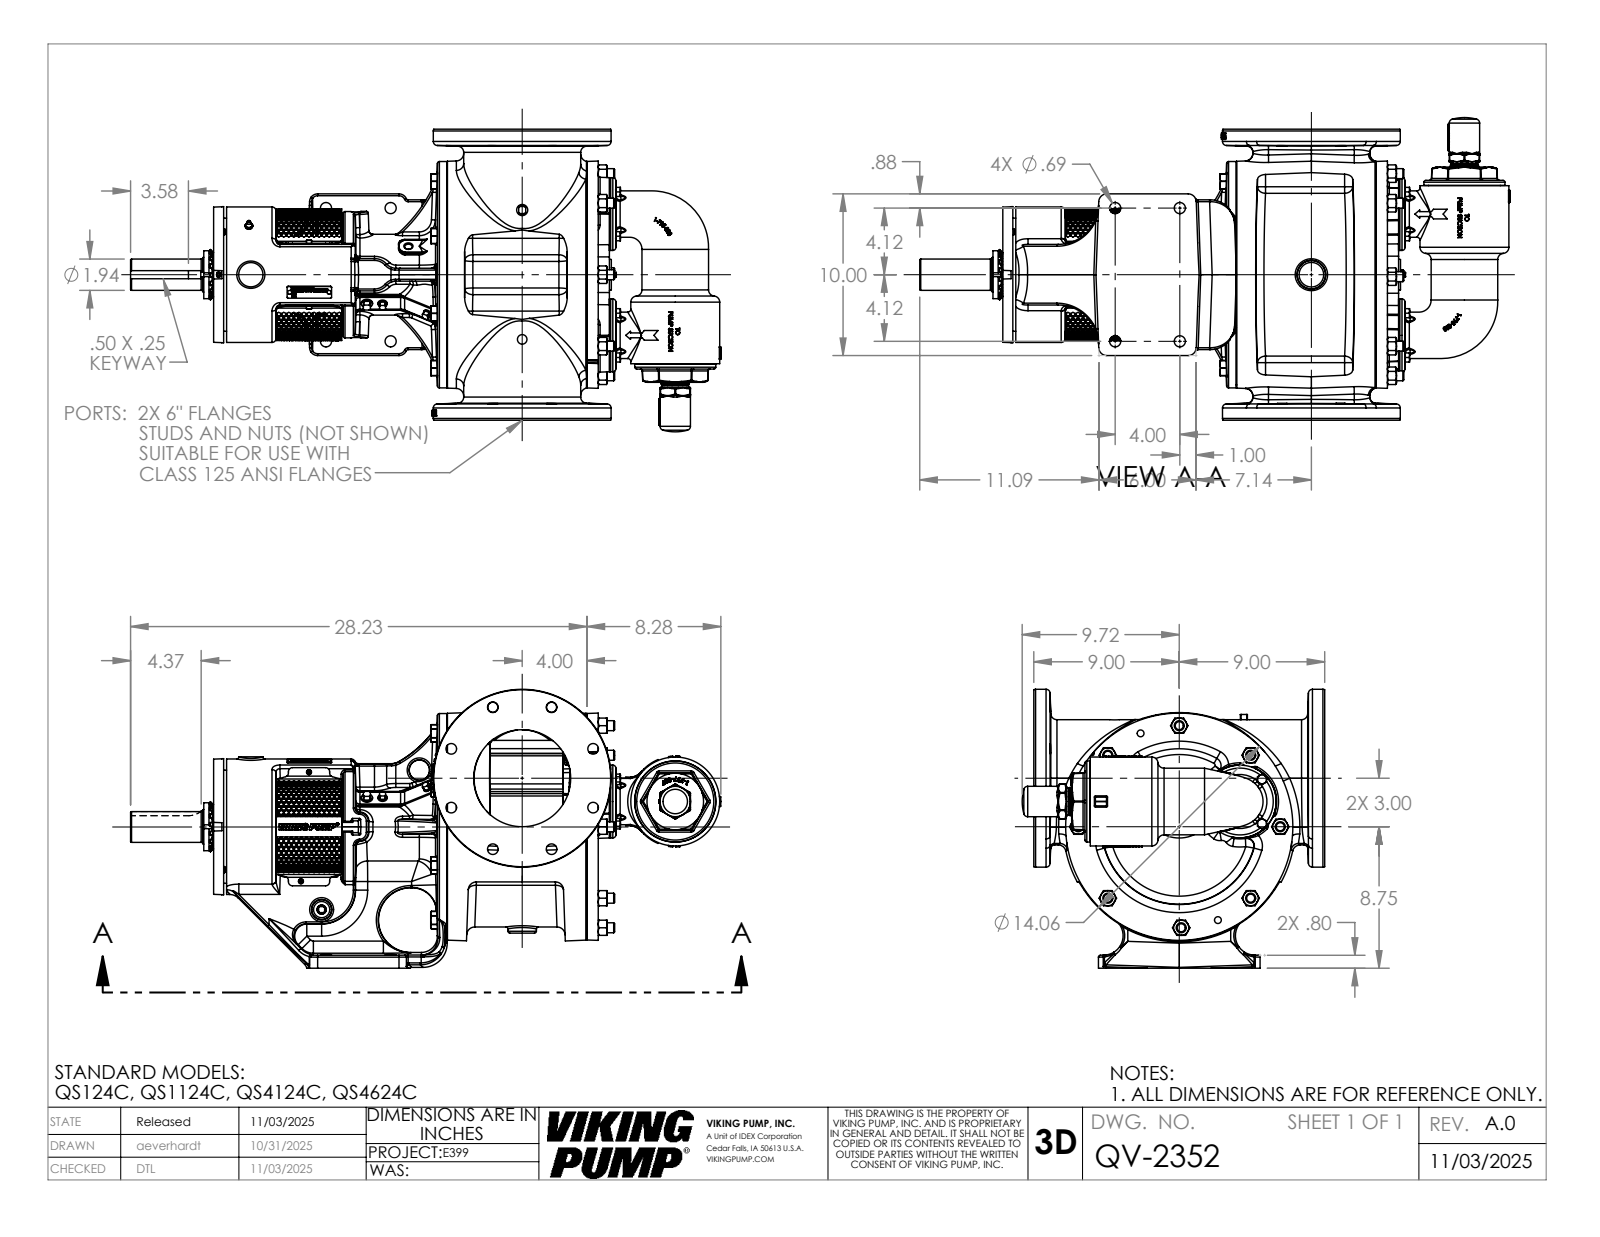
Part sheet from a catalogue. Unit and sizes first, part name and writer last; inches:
Units: inches
Overall size (bounding box): 36.523 × 22.94 × 17.25
Round holes (diameter × count): ⌀0.266 ×8, ⌀0.406 ×8, ⌀0.41 ×8, ⌀0.656 ×8, ⌀1.157 ×8, ⌀0.25 ×6, ⌀0.688 ×4, ⌀0.159 ×2, ⌀0.313 ×2, ⌀0.422 ×2, ⌀0.453 ×1, ⌀2.157 ×1
Round bosses / shafts (diameter × count): ⌀0.375 ×9, ⌀0.75 ×8, ⌀0.742 ×8, ⌀0.617 ×8, ⌀0.312 ×4, ⌀0.437 ×3, ⌀4.5 ×2, ⌀14 ×1
Partial cylindrical surfaces — rounded edges, fillets, slot ends (radius × count): R0.12 ×66, R0.5 ×23, R0.25 ×21, R0.06 ×20, R0.015 ×18, R0.092 ×18, R0.07 ×16, R0.75 ×14
Main face-to-face distances: 1.5, 18, 16.5, 23.798, 15, 3.82, 19.978, 7.953, 4.133, 15.845
Hole centre spacings: 3.75, 2.079, 5.783, 2.713, 3.133, 3.788, 5.423, 5.932
Volume: 2 559 in³ · Surface area: 2 640 in²
Bodies: 1 solid, 4925 faces (1635 planar, 820 cylindrical, 2470 other)
Part name (STEP PRODUCT): QV-2352
STEP written by: SolidWorks 2024 (AUTOMOTIVE_DESIGN)
